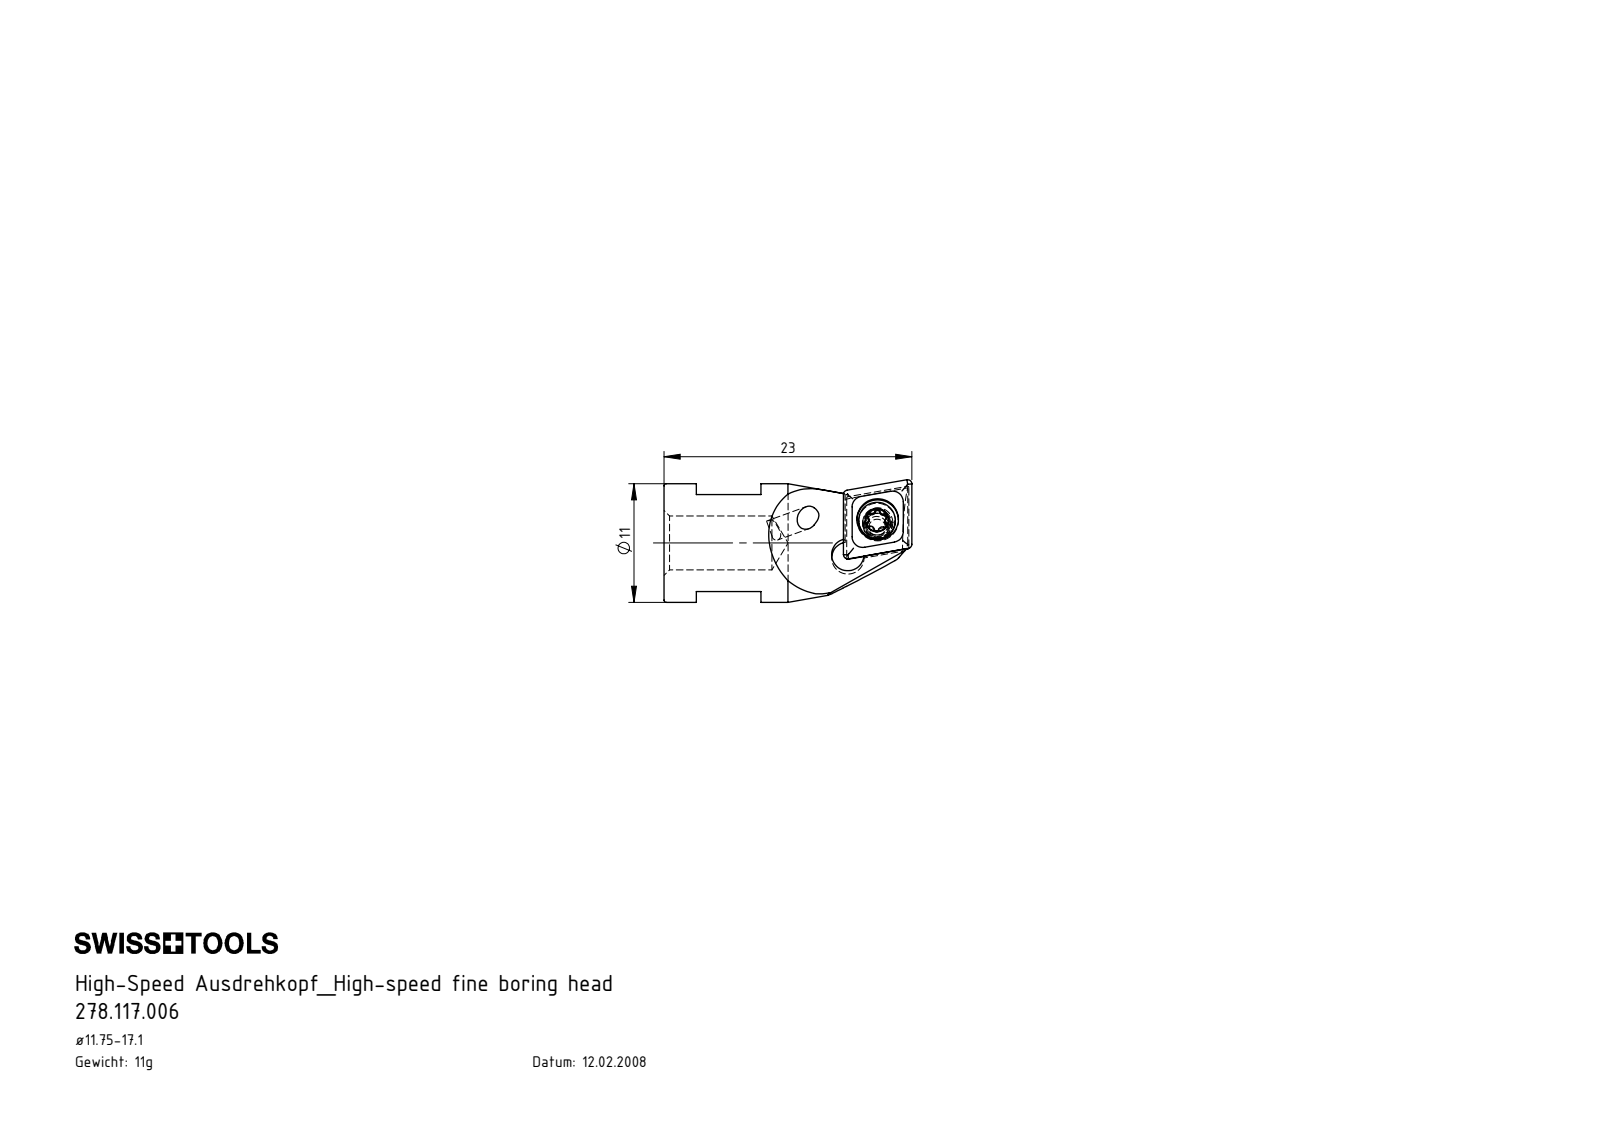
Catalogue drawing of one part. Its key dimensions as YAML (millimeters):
part_name: "HS6-A12.K11.023; CCMT060204; WCA-ER2.001.005_A; HS6-A12.K11.023_B"
step_written_by: "SolidWorks 2017 (CONFIG_CONTROL_DESIGN)"
units: millimeters
bodies: {solids: 3, faces: 123, planar: 34, cylindrical: 35, other: 54}
overall_size: [23, 11.38, 11.02]
volume: 1302
surface_area: 1225
round_holes:
  - {diameter: 2, count: 1}
  - {diameter: 2.05, count: 1}
  - {diameter: 2.8, count: 1}
  - {diameter: 3.85, count: 1}
  - {diameter: 5, count: 1}
round_bosses_or_shafts:
  - {diameter: 11, count: 1}
  - {diameter: 3.4, count: 1}
  - {diameter: 2.5, count: 1}
partial_cylinders:
  - {radius: 0.21, count: 6}
  - {radius: 0.36, count: 5}
  - {radius: 0.36, count: 1}
  - {radius: 1.4, count: 1}
  - {radius: 1.5, count: 1}
  - {radius: 2, count: 1}
face_to_face_distances: [8.99, 2.28, 2.38, 3, 9, 6, 16.8, 13.8, 7.8, 1.48]
